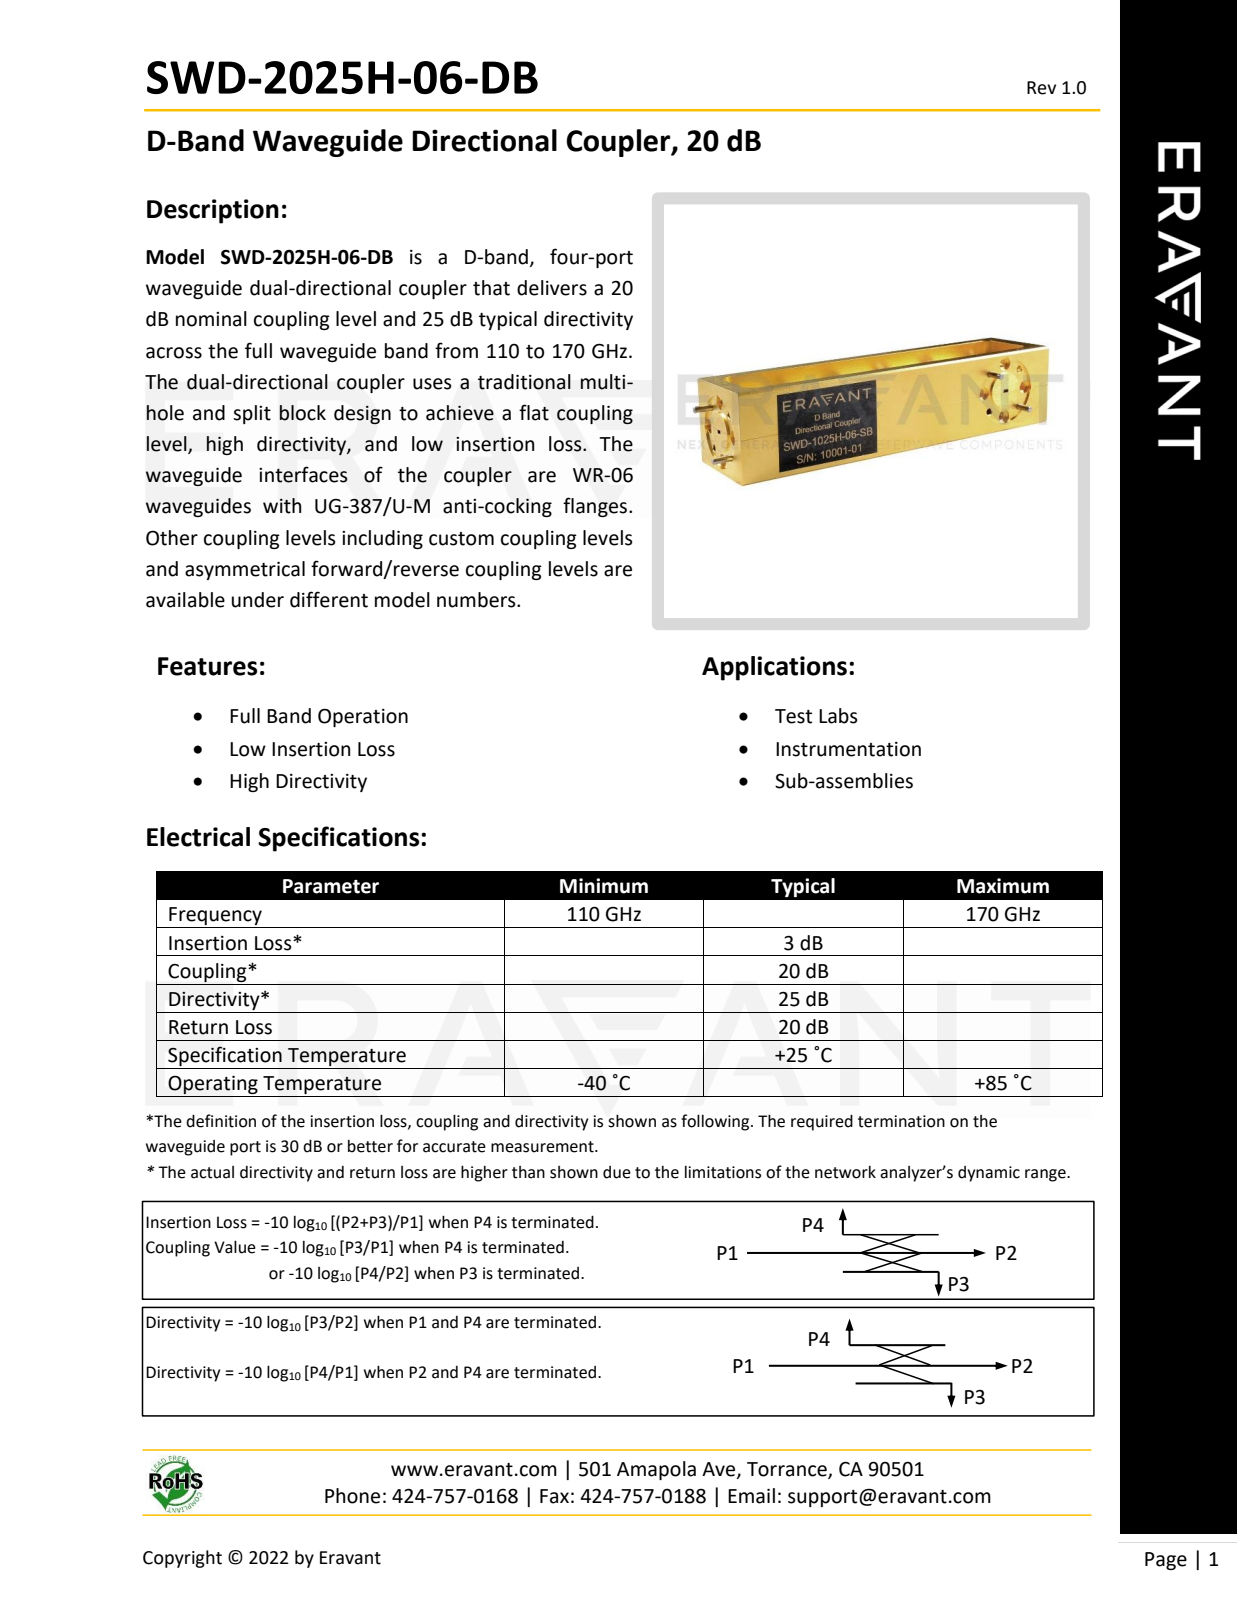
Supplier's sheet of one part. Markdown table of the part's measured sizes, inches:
| quantity | value |
| --- | --- |
| part name | WD-DB-D-A |
| STEP written by | SolidWorks 2021 (CONFIG_CONTROL_DESIGN) |
| units | inches |
| bodies | 63 solids, 1566 faces (596 planar, 484 cylindrical, 486 other) |
| overall size | 3.925 × 1.275 × 0.866 |
| volume | 1.623 in³ |
| surface area | 24.8 in² |
| round holes (diameter × count) | 0.07 × 36, 0.089 × 20, 0.094 × 18, 0.096 × 18, 0.1 × 18, 0.14 × 12, 0.061 × 8, 0.067 × 8, 0.68 × 3 |
| round bosses / shafts (diameter × count) | 0.142 × 18, 0.14 × 18, 0.096 × 18, 0.086 × 18, 0.06 × 18, 0.063 × 8, 0.375 × 2, 0.375 × 1 |
| partial cylindrical surfaces (radius × count) | 0.125 × 4 |
| main face-to-face distances | 0.15, 0.8, 0.95, 0.257, 0.65, 0.28, 0.537, 0.587, 0.867, 0.33 |
| hole center spacings | 0.215, 0.52, 0.398, 0.281, 0.281, 0.398, 0.563, 2.401 |
